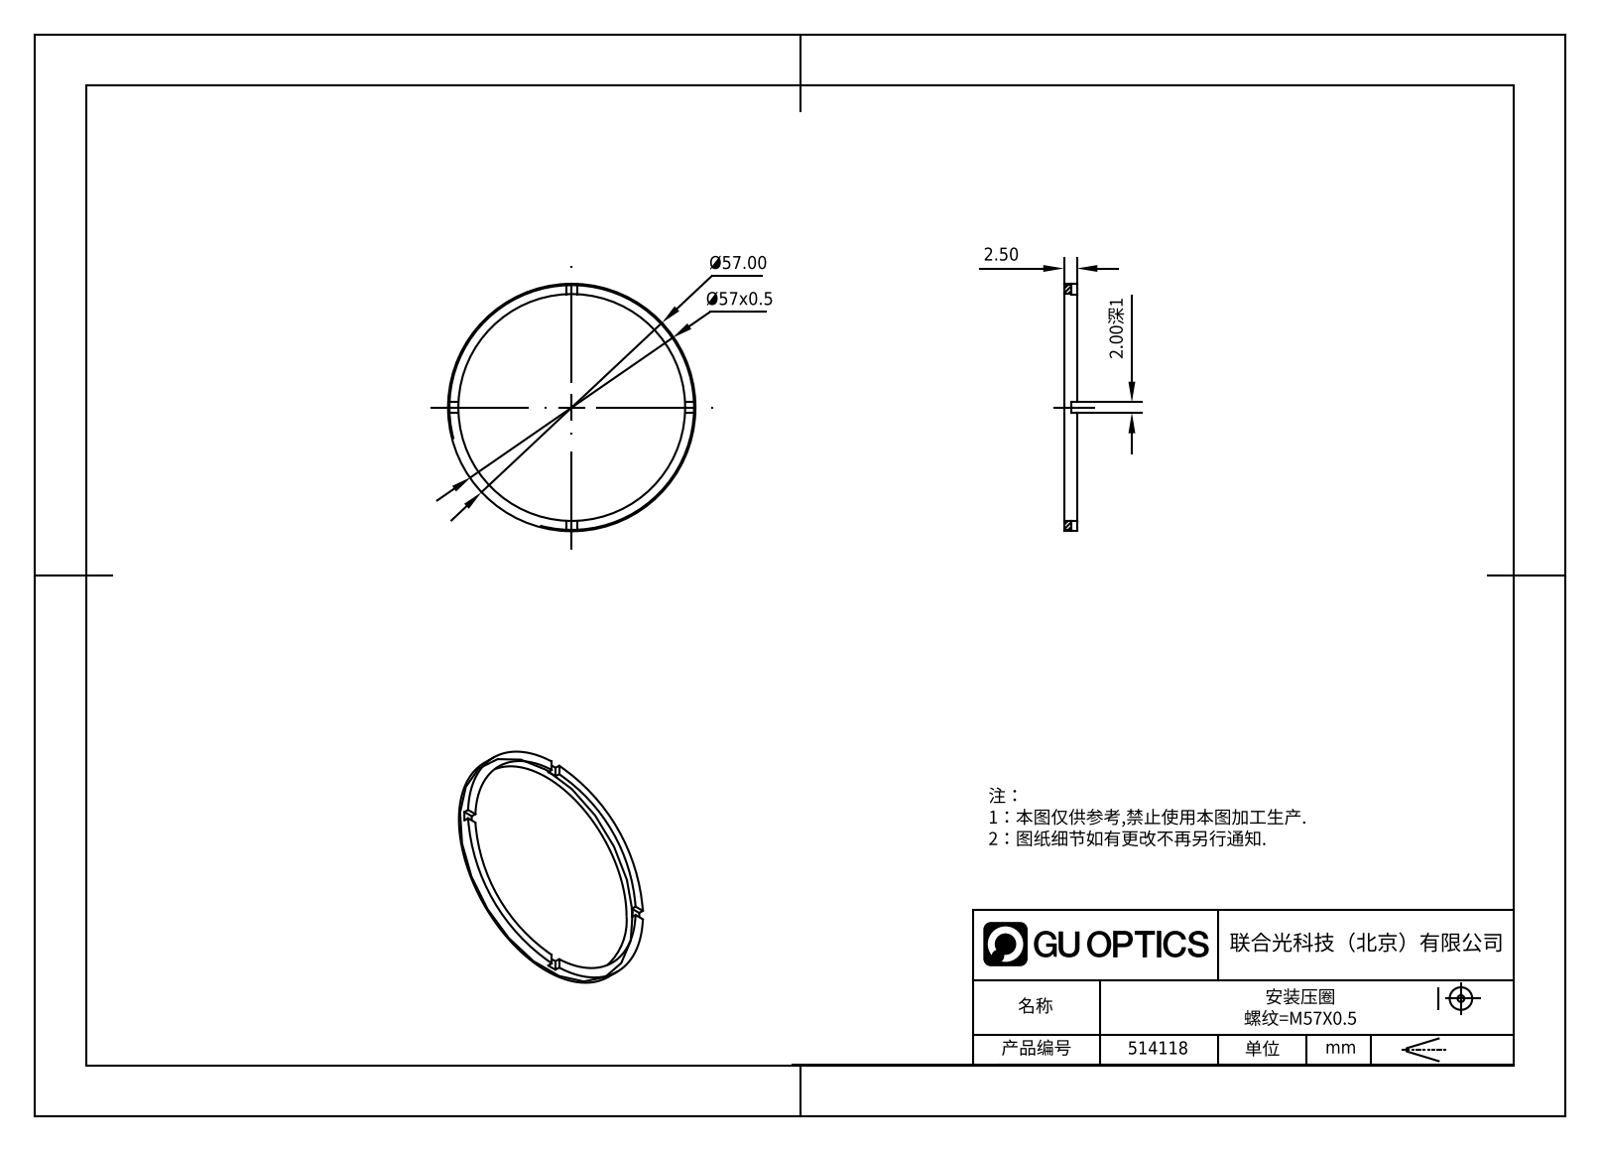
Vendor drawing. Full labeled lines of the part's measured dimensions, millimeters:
Part name (STEP PRODUCT): 514118
STEP written by: SolidWorks 2020 (CONFIG_CONTROL_DESIGN)
Units: millimetres
Bodies: 1 solid, 21 faces (17 planar, 4 cylindrical, 0 other)
Overall size (bounding box): 57 × 57 × 2.5
Volume: 1 050 mm³ · Surface area: 1 716 mm²
Round holes (diameter × count): ⌀52 ×1
Round bosses / shafts (diameter × count): ⌀57 ×1
Main face-to-face distances: 2.5, 1.5, 1, 2
